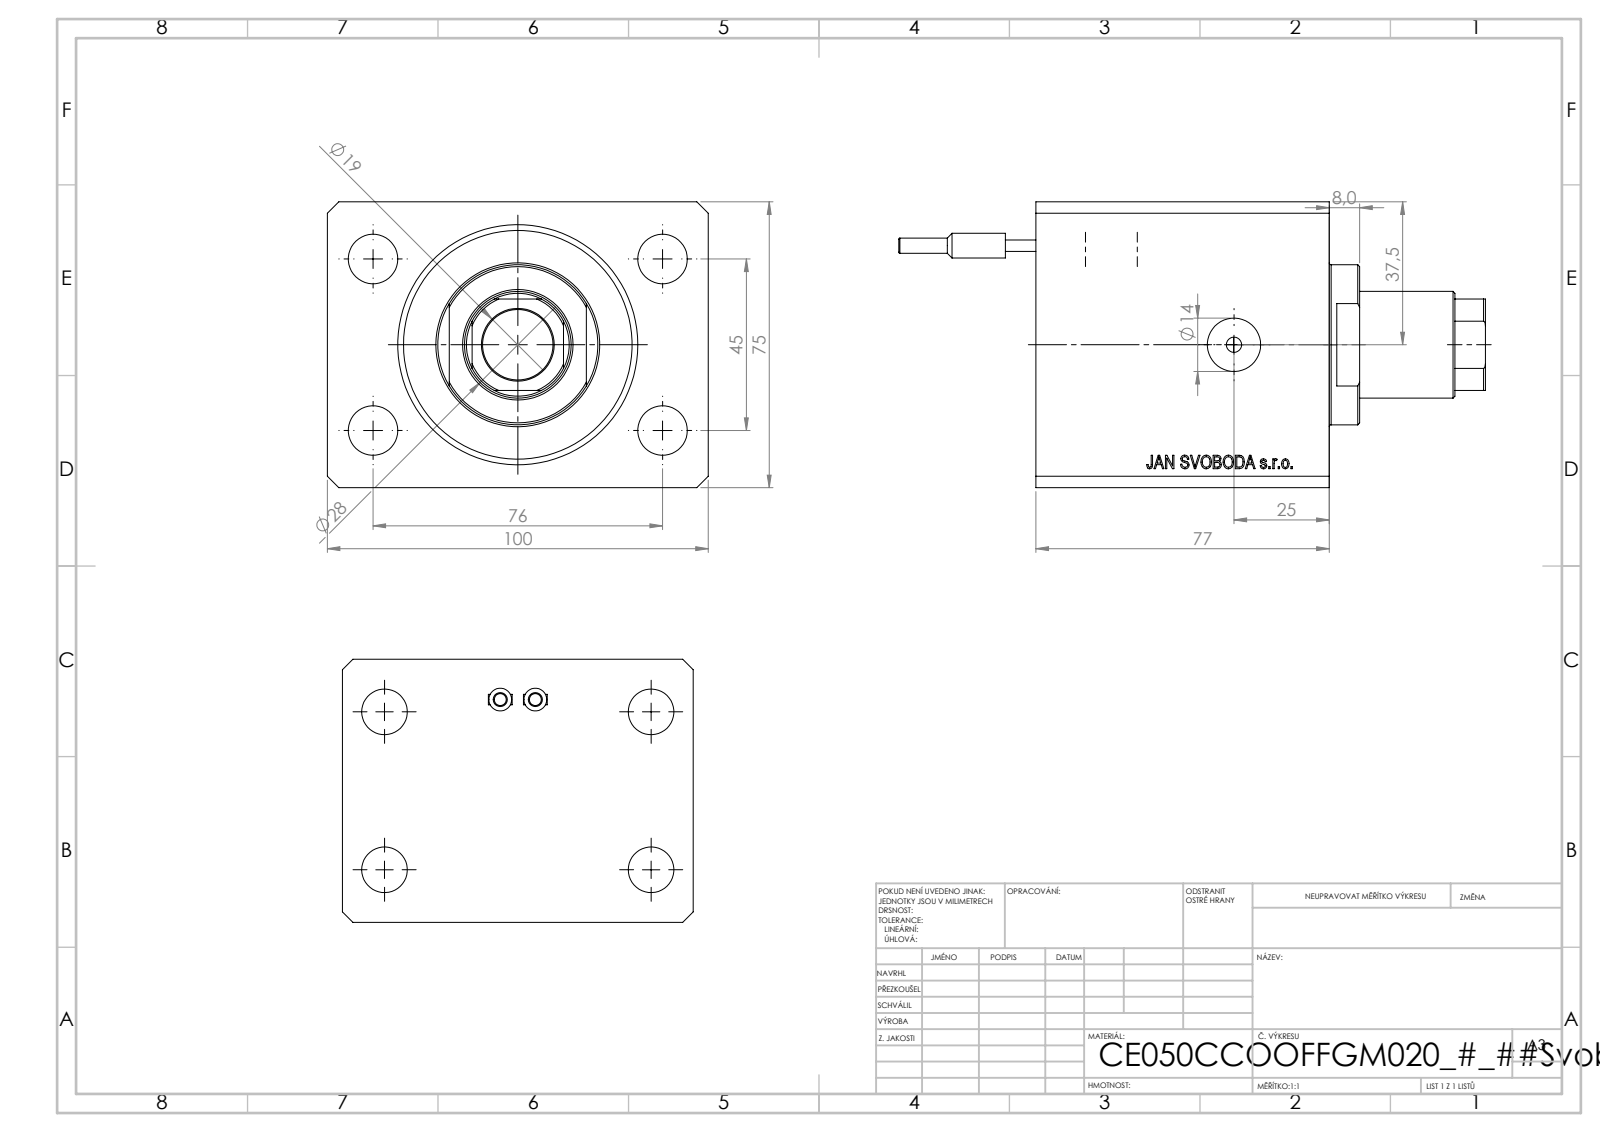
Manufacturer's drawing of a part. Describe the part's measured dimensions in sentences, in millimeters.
The part is named "V250CE_VC_C; V250CE_C_VCP; SWITCH_V250CE; V250CE_C_Body". Its 3-D file was written by "SolidWorks 2019 (CONFIG_CONTROL_DESIGN)". It is 5 solids with 905 faces: 457 planar, 48 cylindrical and 400 other. Overall it measures 154 by 100 by 75 millimeters. Its volume is 563 410 cubic millimeters and its surface area 94 574 square millimeters. Round holes: 4 of diameter 13, 2 of diameter 4, 2 of diameter 14, 1 of diameter 18.5, 1 of diameter 28, 1 of diameter 50, 1 of diameter 63. Round bosses or shafts: 2 of diameter 6.8, 2 of diameter 6.5, 2 of diameter 4, 1 of diameter 42. Partial cylindrical surfaces (rounded edges, fillets, slot ends): 1 of radius 13.5. The main face-to-face distances are 75, 77, 100, 32, 45, 51.9, 19.9, 25.1, 20, 25. The hole center spacings are 44.16, 45, 76, 88.32, 27.
